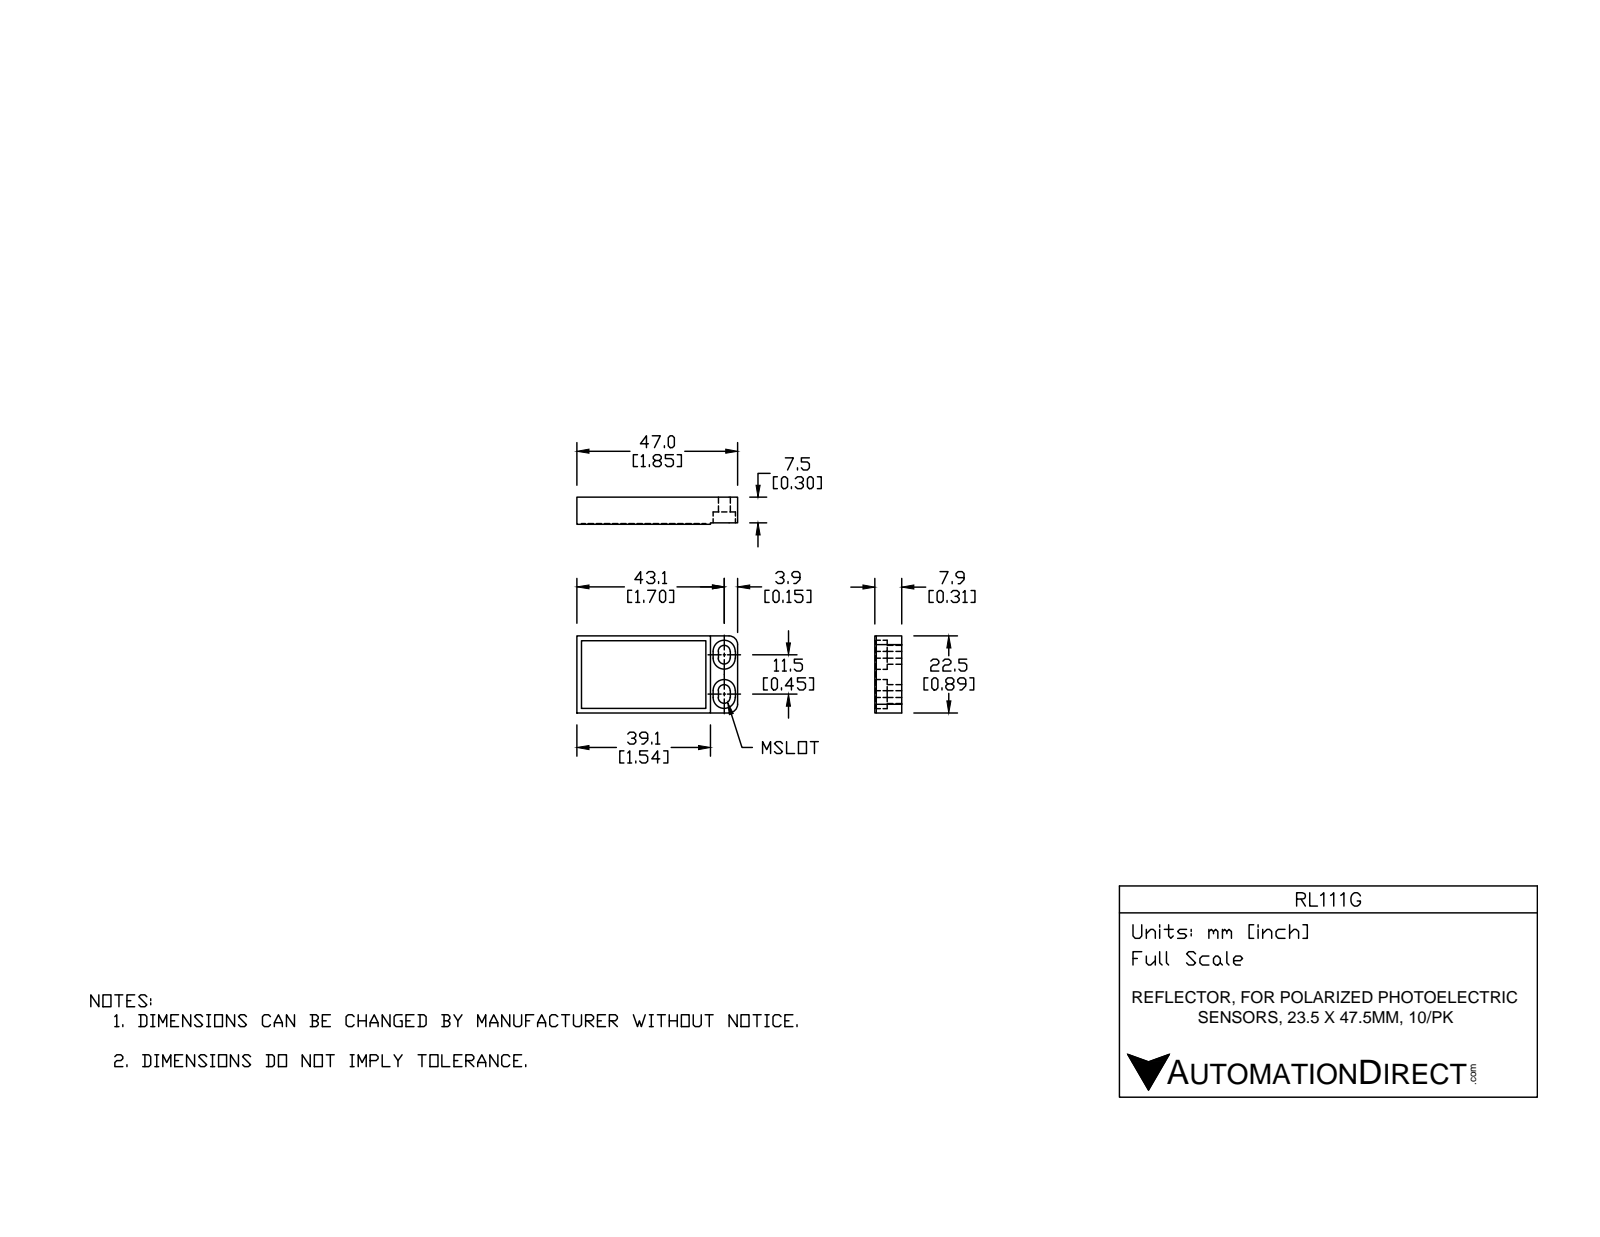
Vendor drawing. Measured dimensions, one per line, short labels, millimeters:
name: RL-111G
written by: SolidWorks 2017 (AUTOMOTIVE_DESIGN)
unit: mm
bodies: 1 solid, 33 faces (23 planar, 10 cylindrical, 0 other)
size: 47 × 22.5 × 7.9
volume: 7 690 mm³; area: 3 426 mm²
rounds: 4× R1.8, 4× R3.3, 2× R2.5
face distances: 7.7, 22.5, 7.9, 47, 7.5, 0.4, 4.3, 3.2, 3.4, 3.6
